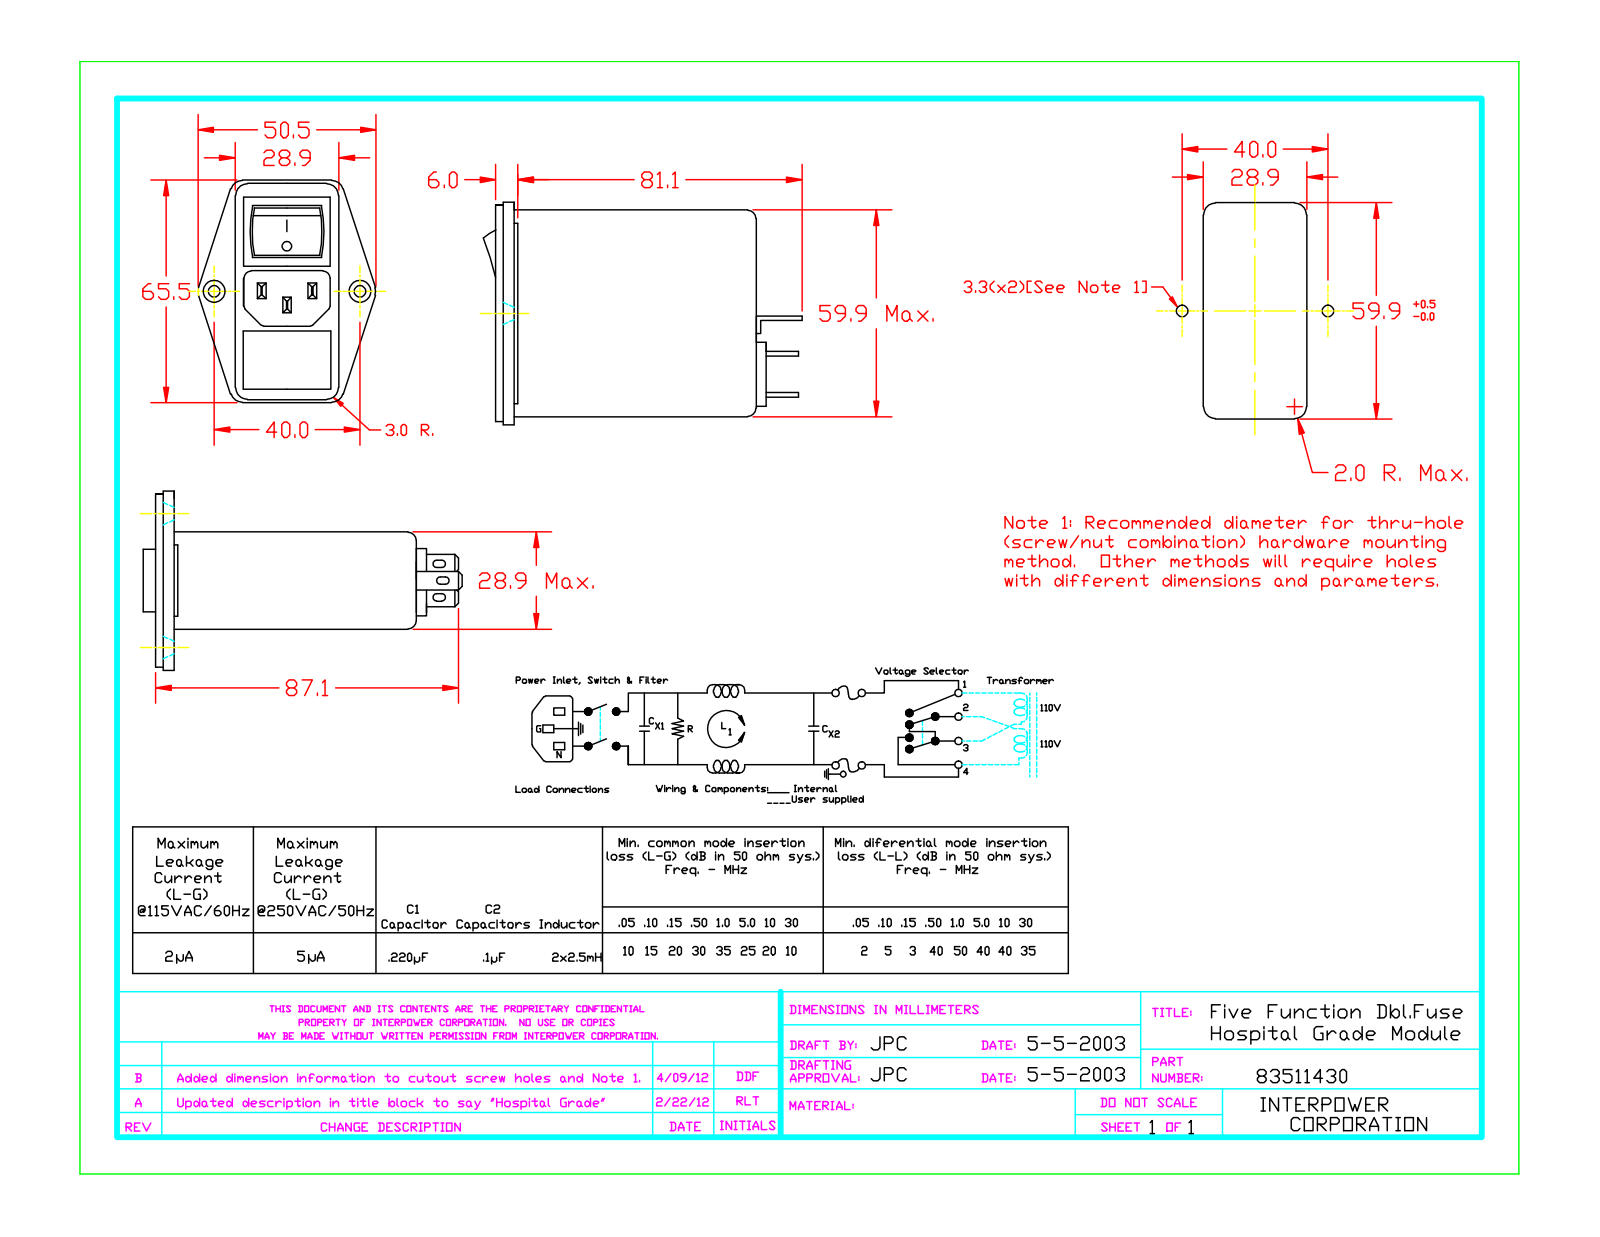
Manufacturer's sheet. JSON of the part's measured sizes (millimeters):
{"part_name": "83511430-R1", "step_written_by": "SolidWorks 2007 (CONFIG_CONTROL_DESIGN)", "units": "millimeters", "bodies": {"solids": 1, "faces": 340, "planar": 221, "cylindrical": 86, "other": 33}, "overall_size": [90.45, 65.5, 50.5], "volume_mm3": 128292, "surface_area_mm2": 22427, "round_holes": [[3.5, 2], [4, 2], [3, 1]], "round_bosses_or_shafts": [[2, 1]], "partial_cylinders_radius": [[0.5, 12], [0.25, 9], [1, 6], [0.85, 4], [1.45, 4], [1.5, 4], [2, 4], [3, 4]], "face_to_face_distances": [28.9, 60.4, 1, 75, 2, 69, 73, 4, 70, 6], "hole_center_spacings": [40]}
